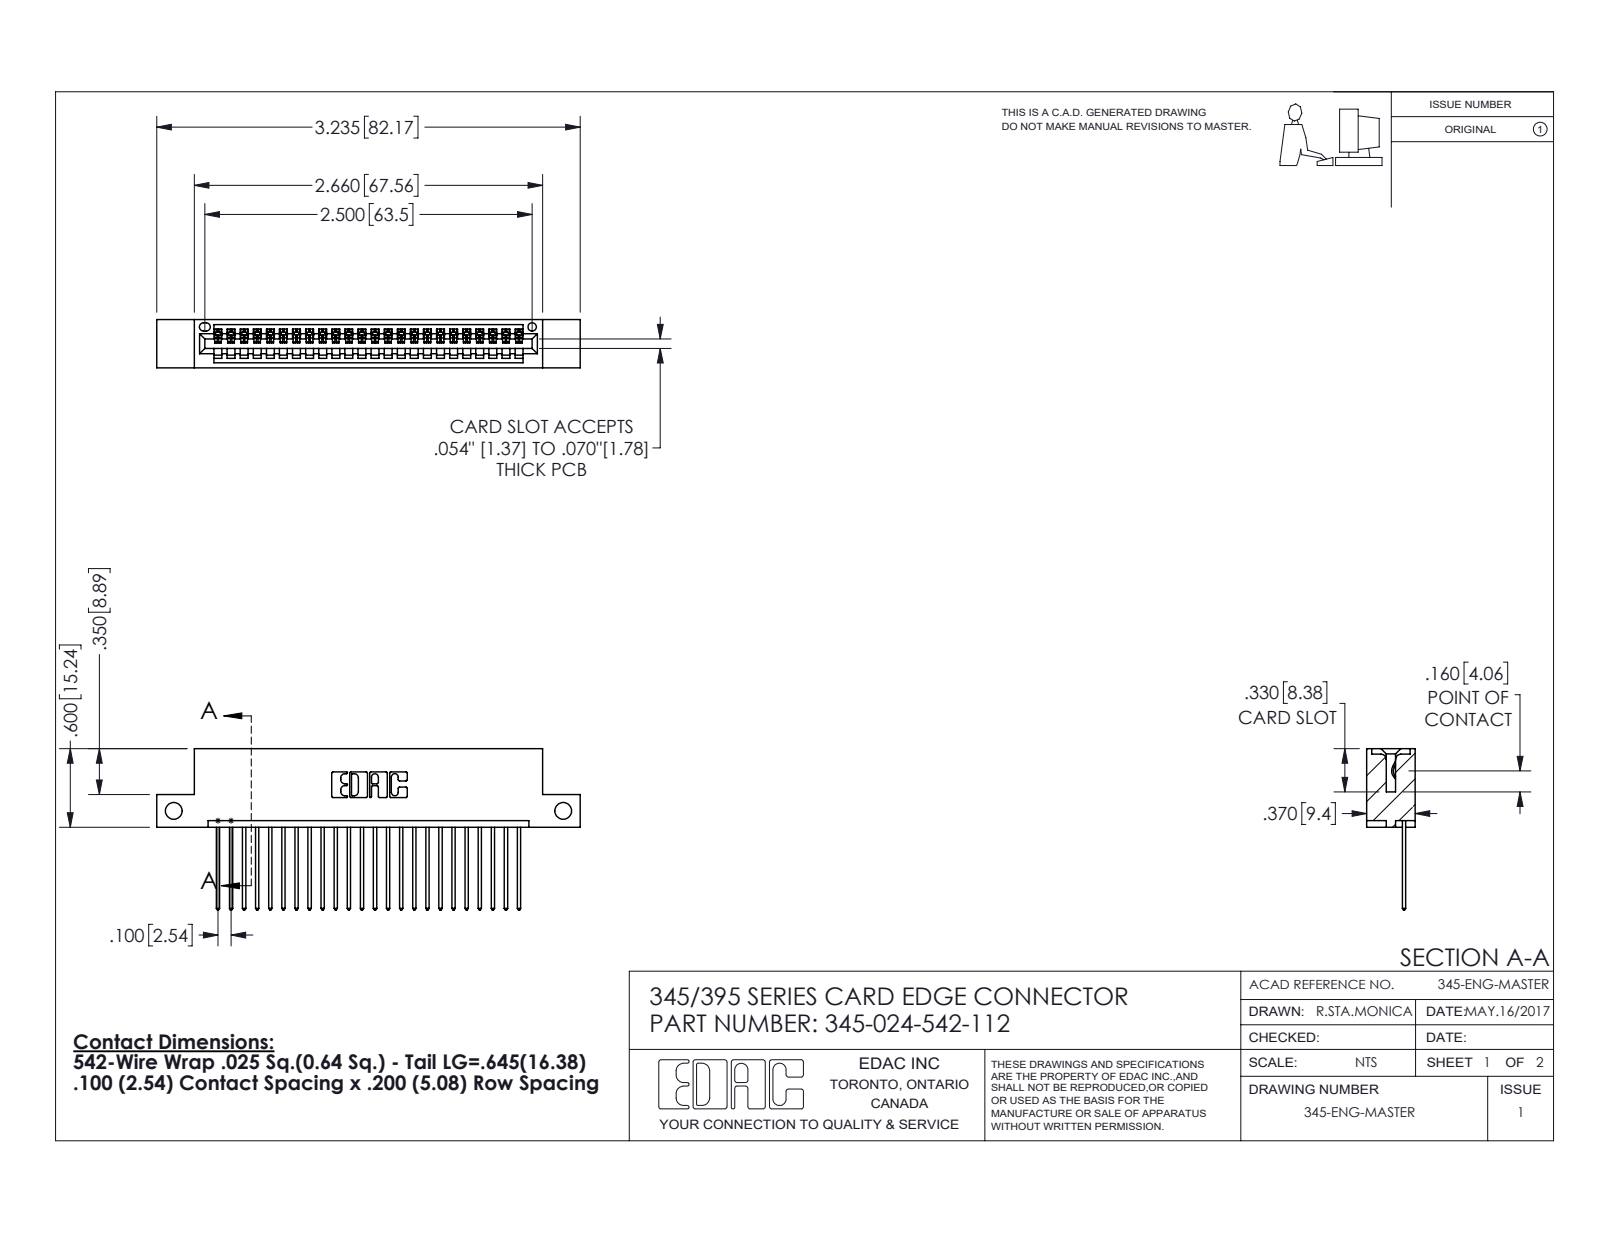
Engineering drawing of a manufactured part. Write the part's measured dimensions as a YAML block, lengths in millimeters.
part_name: "345-292-001_345-293-142; 345 Part_Flush Mounting Lugs - Side Mount; 345-024-542-112"
step_written_by: "SolidWorks 2016 (CONFIG_CONTROL_DESIGN)"
units: millimeters
bodies: {solids: 25, faces: 1518, planar: 1040, cylindrical: 478, other: 0}
overall_size: [82.2, 31.3, 9.4]
volume: 7620
surface_area: 10080
round_holes:
  - {diameter: 3.3, count: 2}
  - {diameter: 1.6, count: 1}
partial_cylinders:
  - {radius: 0.2, count: 48}
  - {radius: 0.3, count: 48}
  - {radius: 0.3, count: 22}
  - {radius: 0.2, count: 6}
  - {radius: 0.8, count: 6}
  - {radius: 0.7, count: 3}
  - {radius: 0.8, count: 2}
  - {radius: 1, count: 2}
face_to_face_distances: [7.6, 1.8, 5.1, 9.4, 2.5, 6.9, 0.6, 5.7, 3.8, 1.8]
hole_center_spacings: [75.6]
